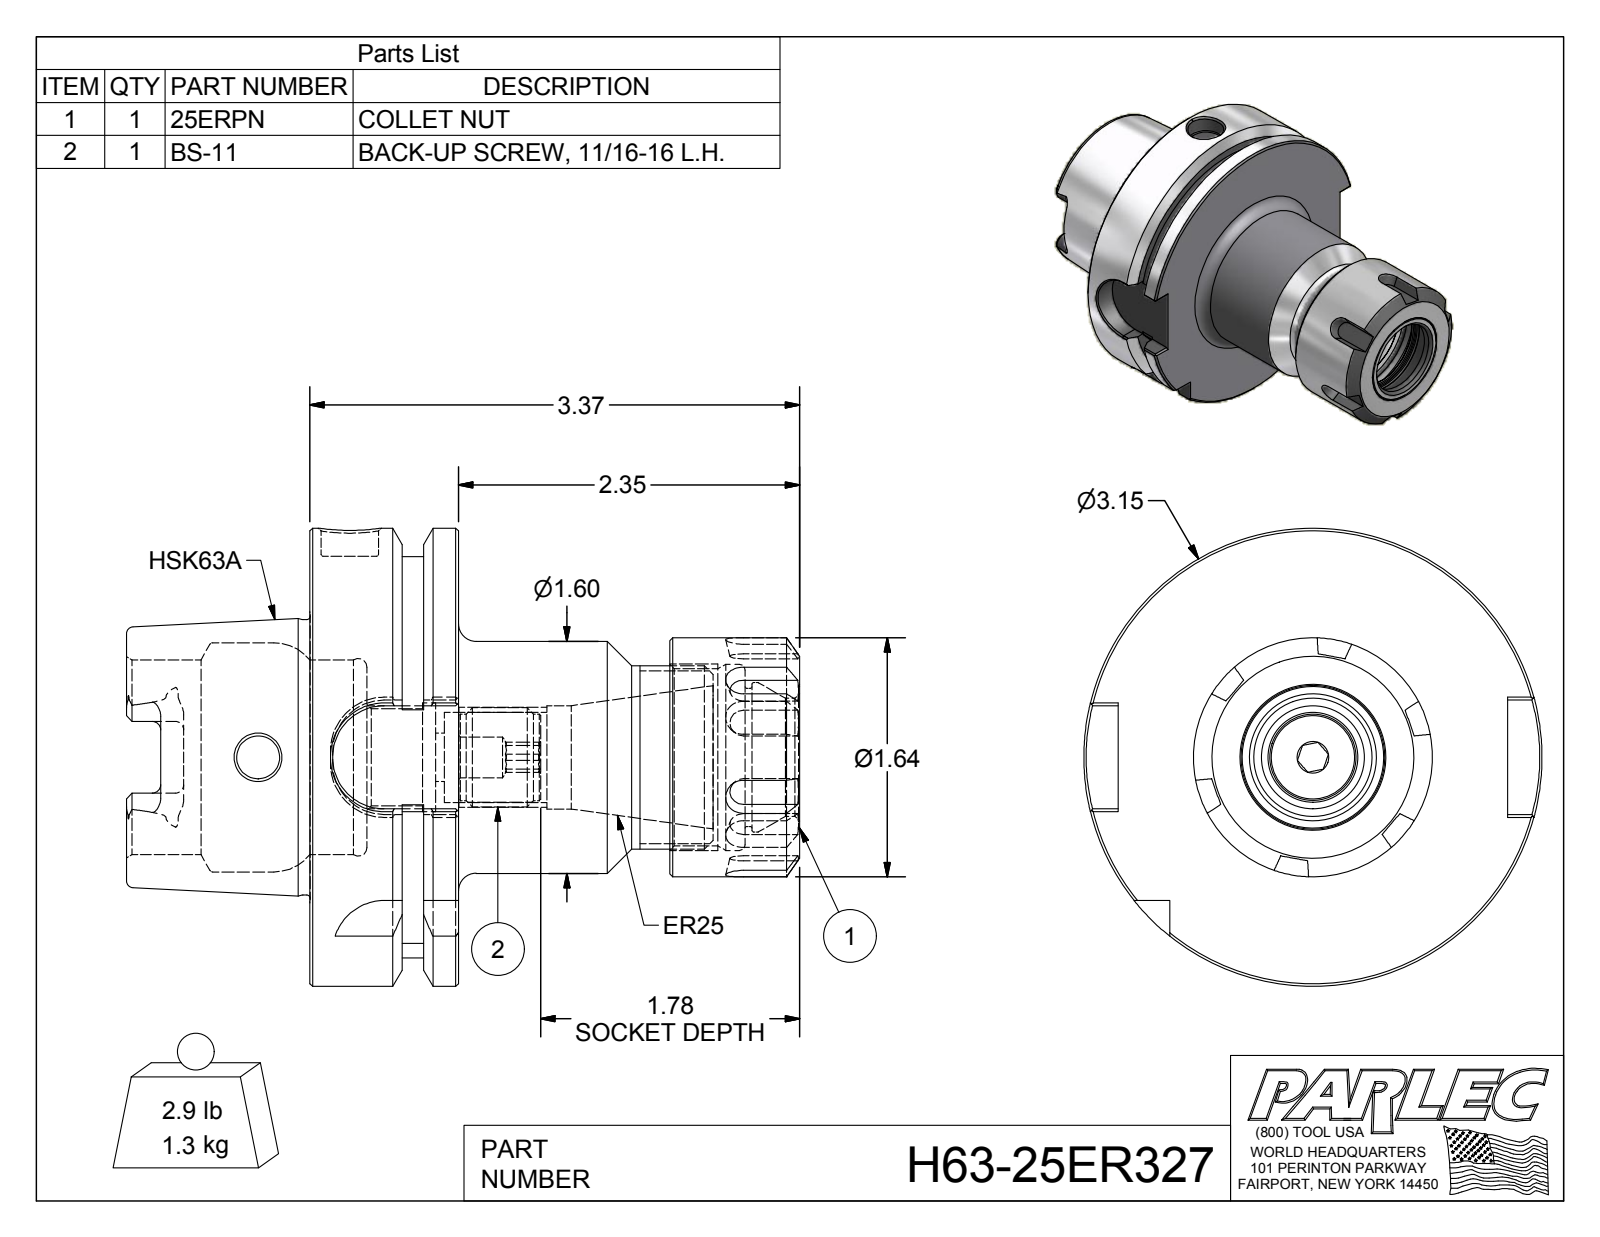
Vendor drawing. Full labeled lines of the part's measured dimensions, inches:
Part name (STEP PRODUCT): H63-25ER327; H63-25ER3-1; BS-11; 25ERPN
STEP written by: Autodesk Inventor 2012 (AUTOMOTIVE_DESIGN)
Units: inches
Bodies: 3 solids, 206 faces (86 planar, 45 cylindrical, 75 other)
Overall size (bounding box): 4.629 × 3.15 × 3.15
Volume: 11.09 in³ · Surface area: 67.94 in²
Round holes (diameter × count): ⌀0.28 ×1, ⌀0.295 ×1, ⌀0.331 ×1, ⌀0.394 ×1, ⌀0.62 ×1, ⌀0.666 ×1, ⌀0.71 ×1, ⌀0.749 ×1, ⌀0.811 ×1, ⌀0.95 ×1, ⌀1.027 ×1, ⌀1.217 ×1
Round bosses / shafts (diameter × count): ⌀3.15 ×1, ⌀1.891 ×1, ⌀1.643 ×1, ⌀1.595 ×1, ⌀1.26 ×1, ⌀0.681 ×1, ⌀0.595 ×1
Partial cylindrical surfaces — rounded edges, fillets, slot ends (radius × count): R0.059 ×6, R0.113 ×4, R0.354 ×4, R1.378 ×1
Main face-to-face distances: 1.024, 0.394, 3.369, 2.345, 0.63, 2.975, 0.783, 0.389, 0.241, 2.586
